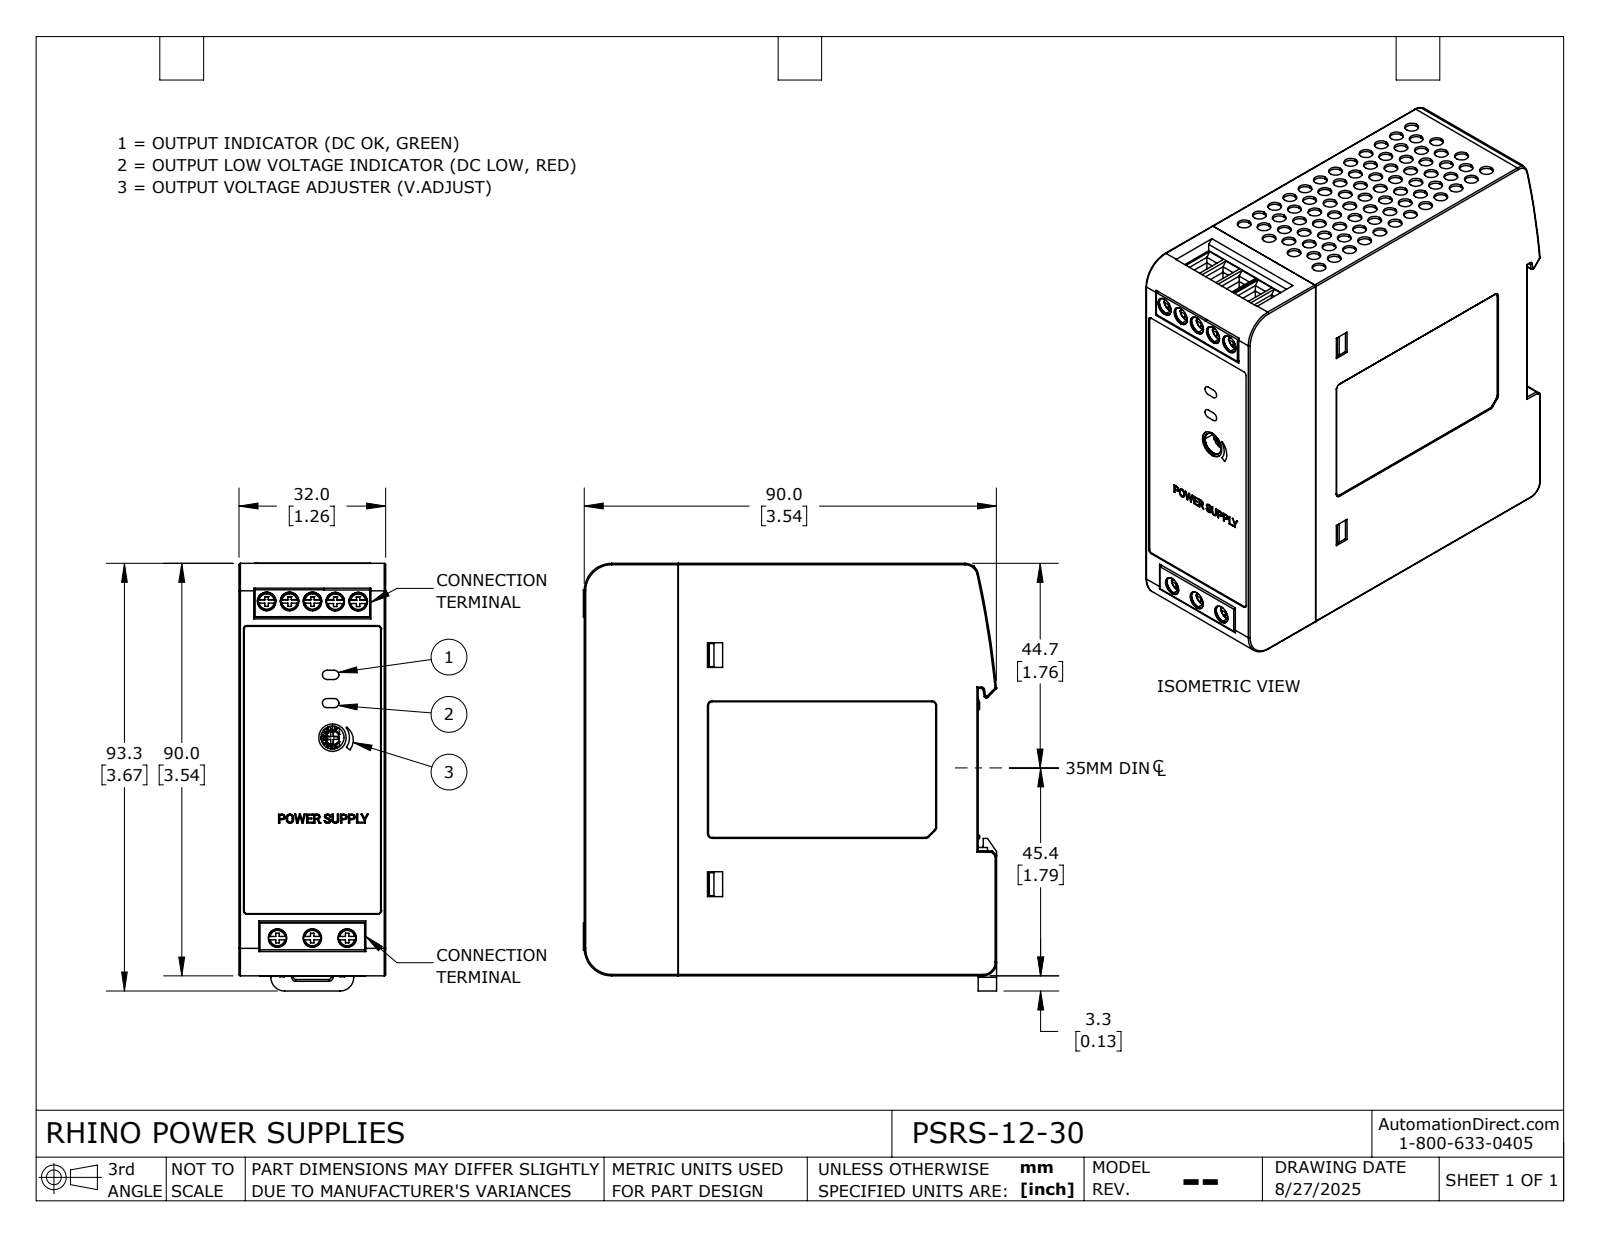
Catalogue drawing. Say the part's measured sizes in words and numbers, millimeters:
The part is named "PSRS-24-30". Its 3-D file was written by "SolidWorks 2024 (AUTOMOTIVE_DESIGN)". It is 1 solid with 1376 faces: 733 planar, 191 cylindrical and 452 other. Overall it measures 93.3 by 90.2 by 32 millimeters. Its volume is 248 207 cubic millimeters and its surface area 32 836 square millimeters. Round holes: 8 of diameter 3.82, 8 of diameter 4.05, 1 of diameter 3.4, 1 of diameter 5. Round bosses or shafts: 8 of diameter 3.95, 1 of diameter 3. Partial cylindrical surfaces (rounded edges, fillets, slot ends): 49 of radius 0.3, 12 of radius 1, 7 of radius 0.5, 6 of radius 0.1, 4 of radius 3, 3 of radius 2.5, 2 of radius 0.6, 2 of radius 5.5. The main face-to-face distances are 32, 90, 31.85, 85.85, 0.5, 89.5, 4, 89.85, 89, 2. The hole center spacings are 5, 7.6, 9.97, 14.97, 43.87, 73.43, 4.97, 10.
